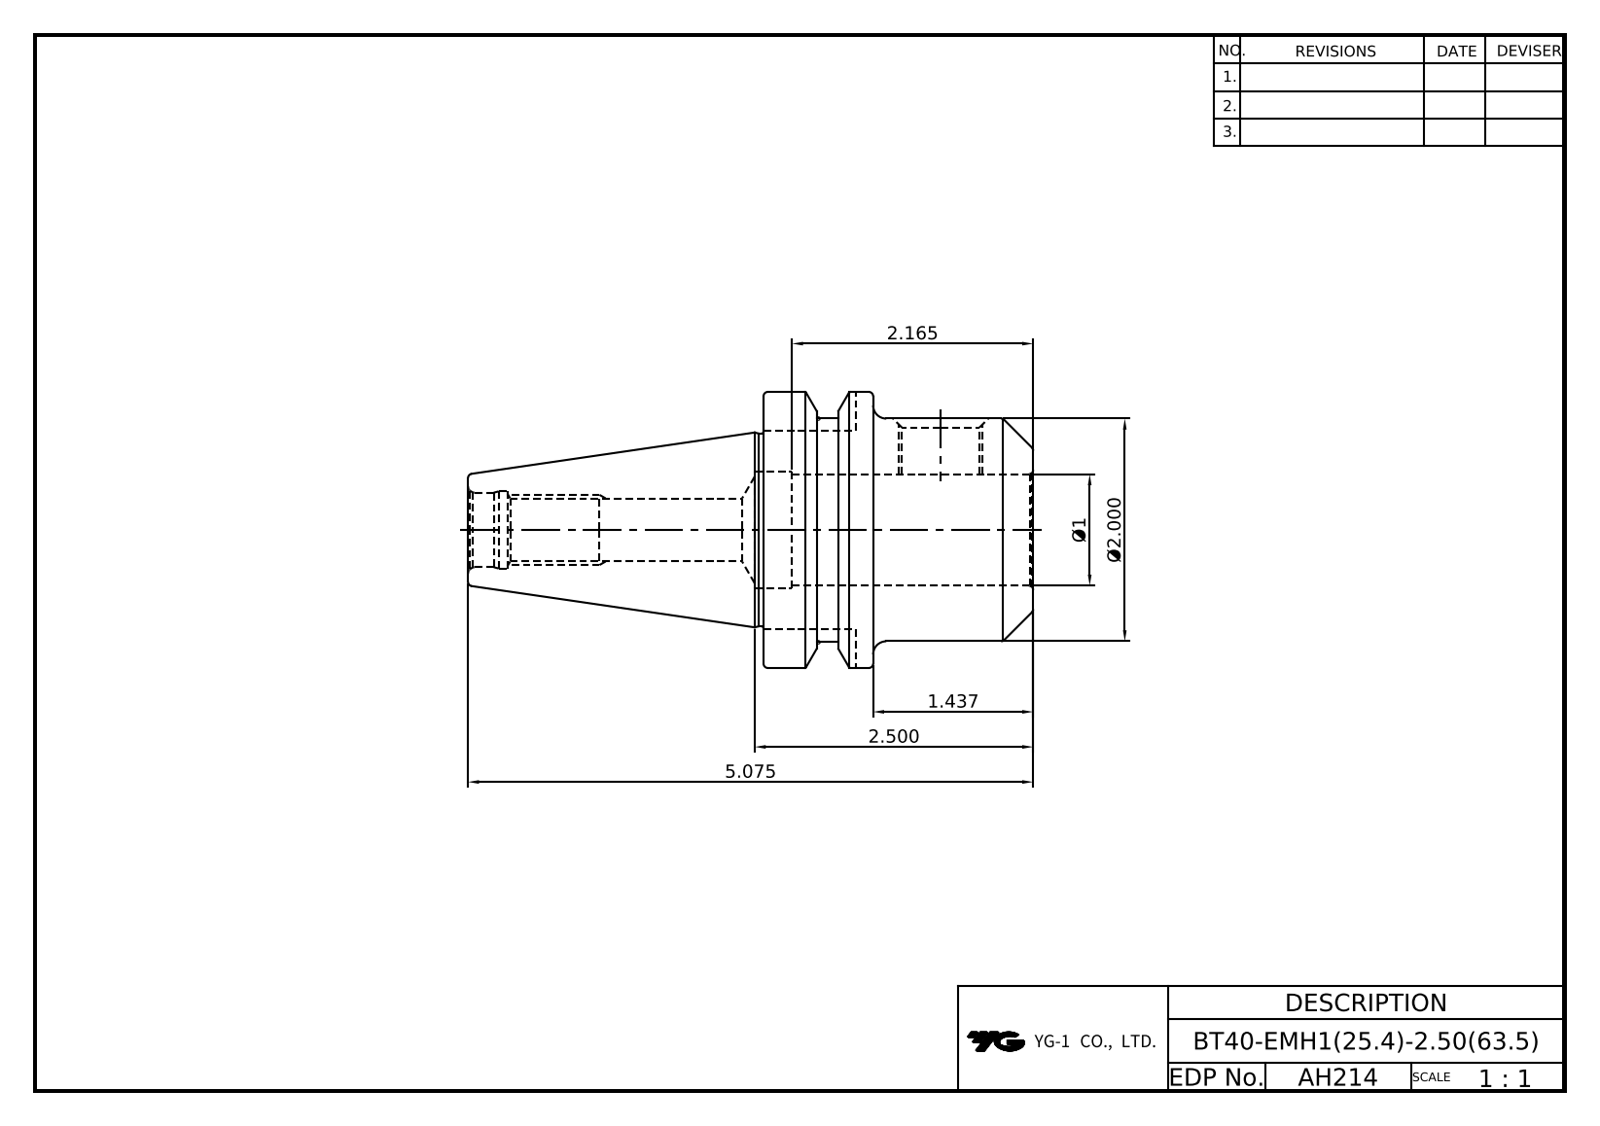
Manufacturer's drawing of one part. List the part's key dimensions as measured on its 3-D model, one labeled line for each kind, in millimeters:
Part name (STEP PRODUCT): BT40-EMH25.4-63.5
STEP written by: Autodesk Inventor 2020 (AUTOMOTIVE_DESIGN)
Units: millimetres
Bodies: 1 solid, 55 faces (18 planar, 16 cylindrical, 21 other)
Overall size (bounding box): 128.9 × 63 × 63
Volume: 156 345 mm³ · Surface area: 31 859 mm²
Round holes (diameter × count): ⌀13.84 ×1, ⌀17 ×1, ⌀17.32 ×1, ⌀17.6 ×1, ⌀25.4 ×1, ⌀26.6 ×1
Round bosses / shafts (diameter × count): ⌀63 ×1, ⌀51 ×1, ⌀50.8 ×1, ⌀44 ×1
Partial cylindrical surfaces — rounded edges, fillets, slot ends (radius × count): R8.05 ×1, R12.5 ×1
Main face-to-face distances: 61.5, 2, 63.5, 27, 25, 36.5, 45.2, 19.1, 17.1, 7.9
